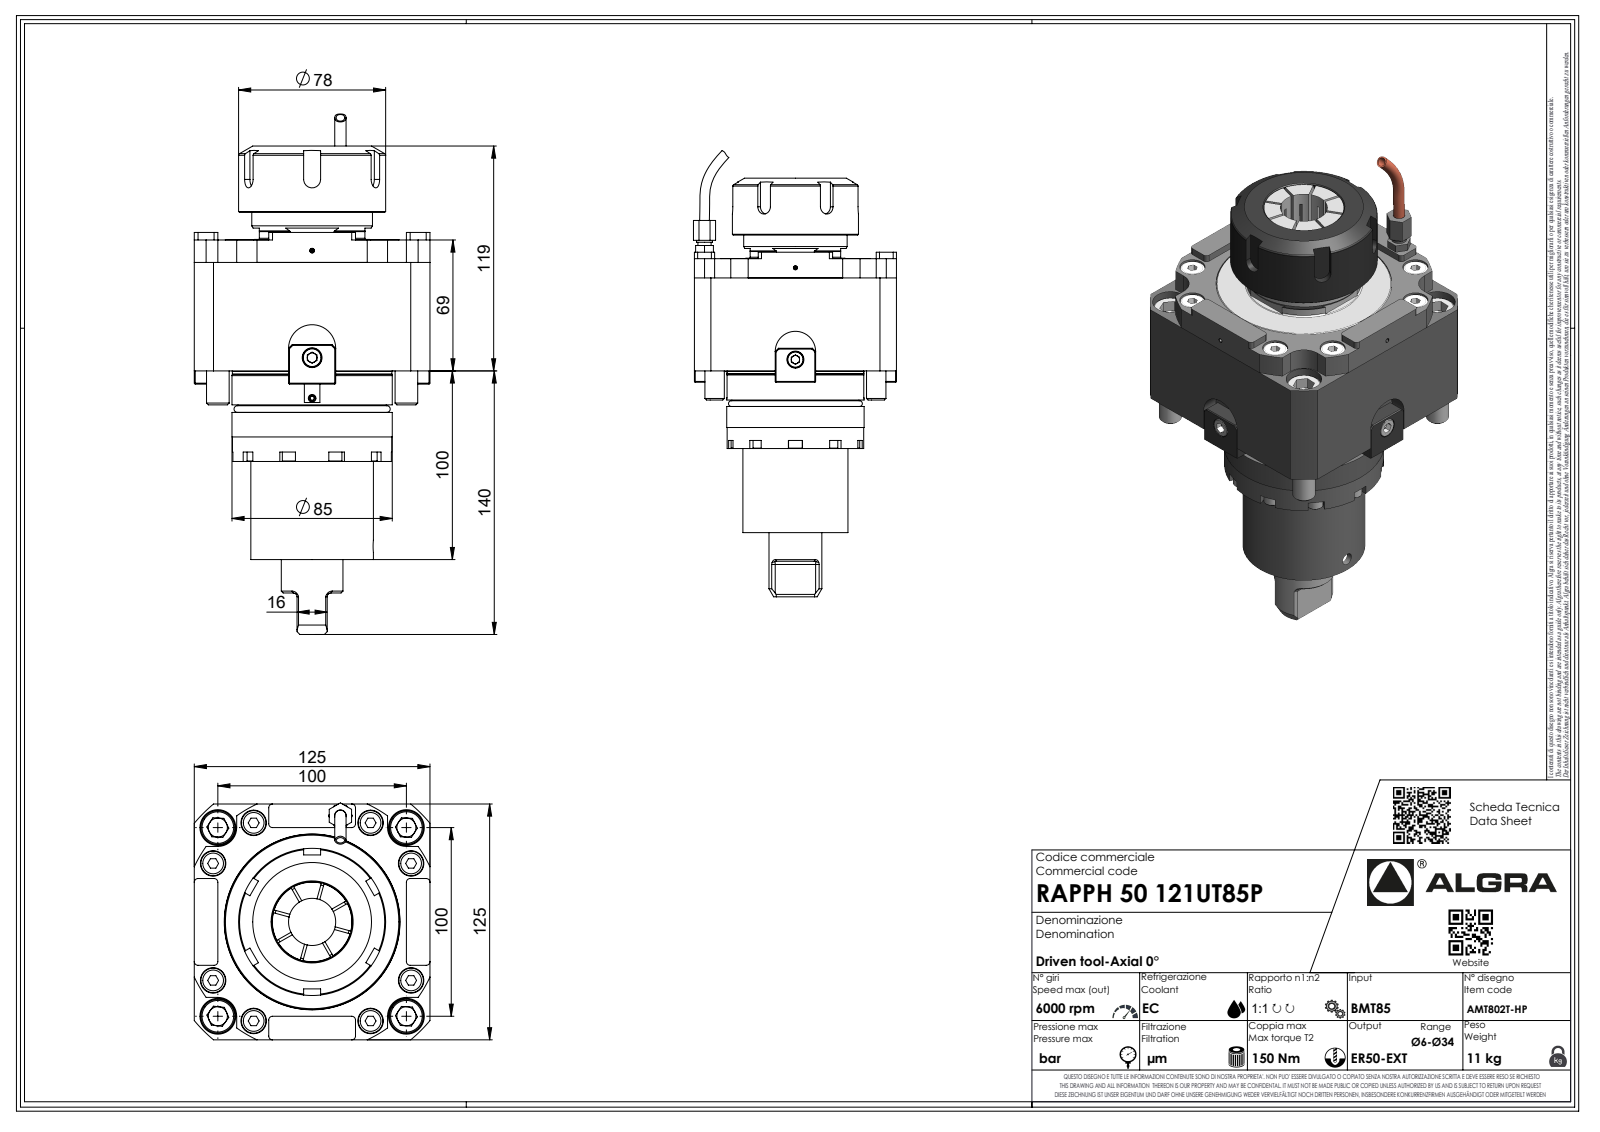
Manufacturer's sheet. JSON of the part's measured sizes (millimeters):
{"part_name": "RAPPH50121UT85P", "step_written_by": "SolidWorks 2023 (AUTOMOTIVE_DESIGN)", "units": "millimeters", "bodies": {"solids": 1, "faces": 580, "planar": 376, "cylindrical": 93, "other": 111}, "overall_size": [258.9, 125, 125], "volume_mm3": 1740000, "surface_area_mm2": 112689, "round_holes": [[2.1, 1]], "round_bosses_or_shafts": [[12, 3], [85, 1], [84.5, 1], [78, 1], [65, 1], [64, 1], [32.7, 1], [6.37, 1]], "partial_cylinders_radius": [[2, 22], [4.35, 10], [0.33, 7], [0.52, 7], [3.7, 7], [10, 4], [4.5, 3], [0.21, 1]], "face_to_face_distances": [125, 69.4, 69.5, 119.2, 49.8, 49.7, 100, 12, 169.4, 169.5]}
